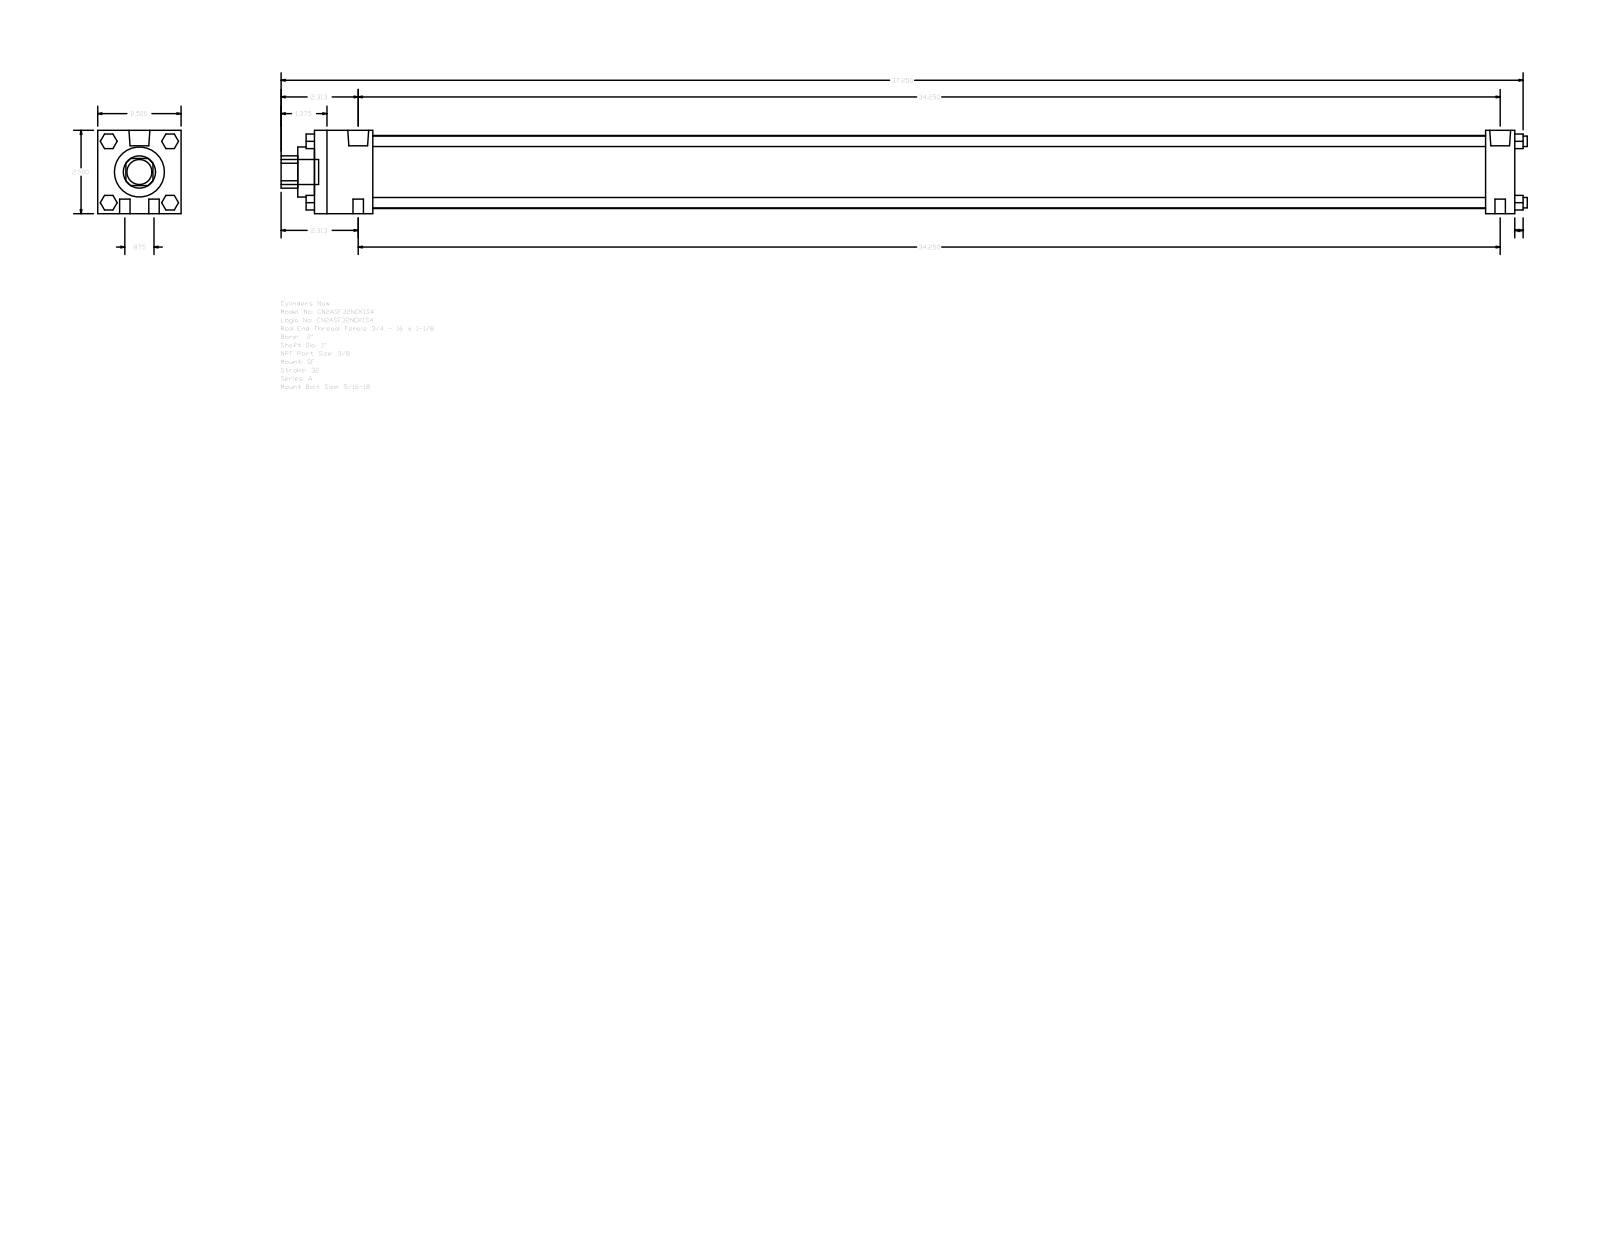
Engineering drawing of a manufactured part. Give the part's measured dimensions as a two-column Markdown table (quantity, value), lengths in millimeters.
| quantity | value |
| --- | --- |
| part name | A_SF__0200_1 |
| STEP written by | GSSL Pune (CONFIG_CONTROL_DESIGN) |
| units | millimeters |
| bodies | 0 solids, 124 faces (94 planar, 30 cylindrical, 0 other) |
| overall size | 949.33 × 63.5 × 63.5 |
| round holes (diameter × count) | 25.4 × 1, 38.1 × 1, 55.63 × 1 |
| round bosses / shafts (diameter × count) | 7.94 × 8, 15.93 × 2, 5.56 × 2, 19.05 × 1 |
| partial cylindrical surfaces (radius × count) | 12.29 × 1 |
| main face-to-face distances | 63.5, 914.4, 892.18, 22.22, 44.45, 847.73, 869.95, 12.7, 927.1, 6.35 |
